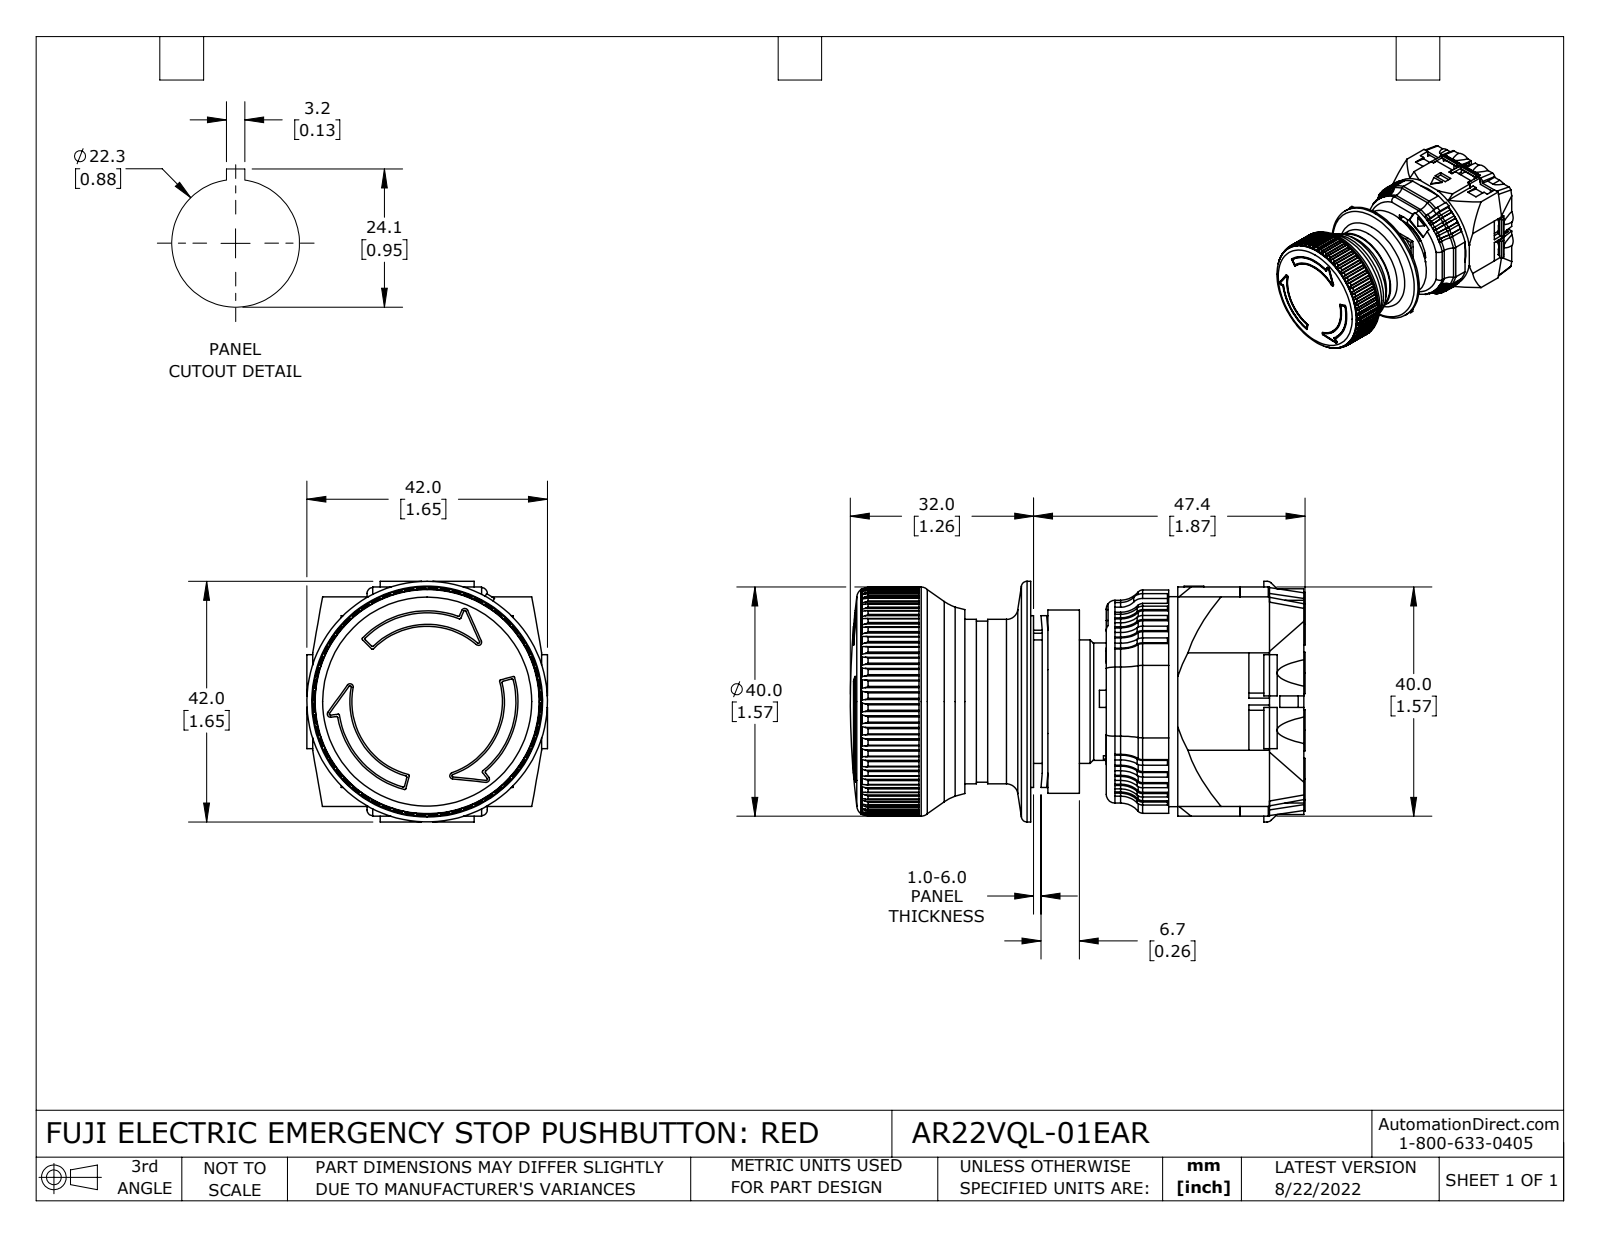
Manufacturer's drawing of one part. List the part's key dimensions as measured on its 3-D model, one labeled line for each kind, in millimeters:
Part name (STEP PRODUCT): AR22VQL-01EAR
STEP written by: SolidWorks 2021 (CONFIG_CONTROL_DESIGN)
Units: millimetres
Bodies: 8 solids, 1459 faces (645 planar, 600 cylindrical, 214 other)
Overall size (bounding box): 79.4 × 42 × 42
Volume: 62 430 mm³ · Surface area: 34 710 mm²
Round holes (diameter × count): ⌀3.5 ×12, ⌀6.2 ×12, ⌀8 ×1, ⌀17.5 ×1, ⌀21 ×1, ⌀21.3 ×1, ⌀22 ×1, ⌀22.3 ×1, ⌀28 ×1, ⌀29.7 ×1, ⌀36.7 ×1
Round bosses / shafts (diameter × count): ⌀7.2 ×12, ⌀42 ×1, ⌀40 ×1, ⌀32 ×1, ⌀30 ×1, ⌀28.7 ×1, ⌀28.1 ×1, ⌀22.4 ×1
Partial cylindrical surfaces — rounded edges, fillets, slot ends (radius × count): R0.2 ×146, R0.4 ×64, R1.2 ×19, R3.8 ×19, R4.2 ×12, R1 ×10, R0.6 ×6, R1.5 ×4
Main face-to-face distances: 1, 18.5, 11.5, 10, 44.7, 18, 21, 3, 23.6, 4
Hole centre spacings: 16.3, 23, 8.3, 8.9, 10, 14.9, 18.1, 18.7
